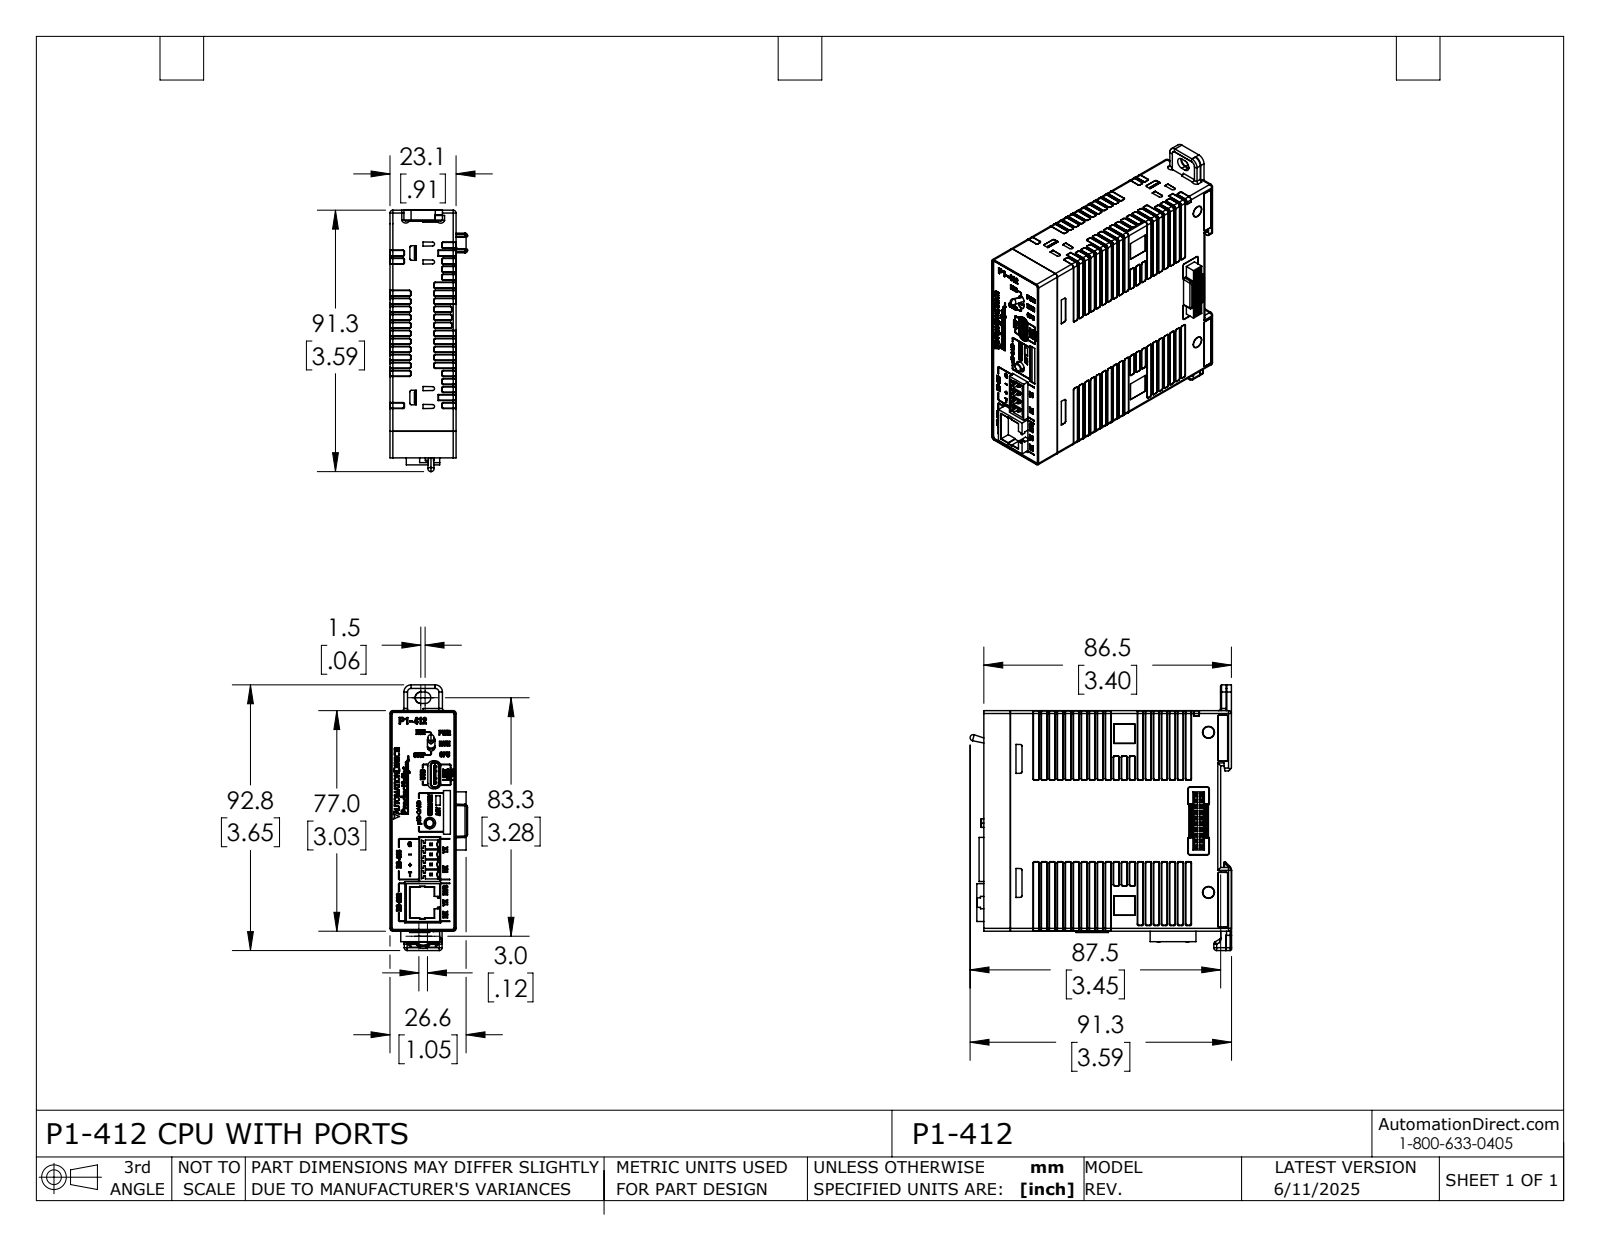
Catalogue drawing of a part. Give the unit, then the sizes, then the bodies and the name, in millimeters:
Units: millimetres
Overall size (bounding box): 92.8 × 91.3 × 27.1
Round holes (diameter × count): ⌀0.6 ×2, ⌀3.1 ×1, ⌀4 ×1
Round bosses / shafts (diameter × count): ⌀3 ×1
Partial cylindrical surfaces — rounded edges, fillets, slot ends (radius × count): R0.3 ×218, R0.5 ×102, R1 ×39, R0.2 ×30, R0.4 ×10, R0.7 ×10, R0.8 ×7, R2 ×7
Main face-to-face distances: 23.1, 23, 8.9, 15.8, 6.9, 23, 0.5, 77, 16.1, 9.2
Hole centre spacings: 2, 7.4, 10.5, 18, 27.8, 35.2, 45.7
Volume: 162 600 mm³ · Surface area: 32 030 mm²
Bodies: 5 solids, 4725 faces (2287 planar, 966 cylindrical, 1472 other)
Part name (STEP PRODUCT): P1-412
STEP written by: SolidWorks 2024 (AUTOMOTIVE_DESIGN)
